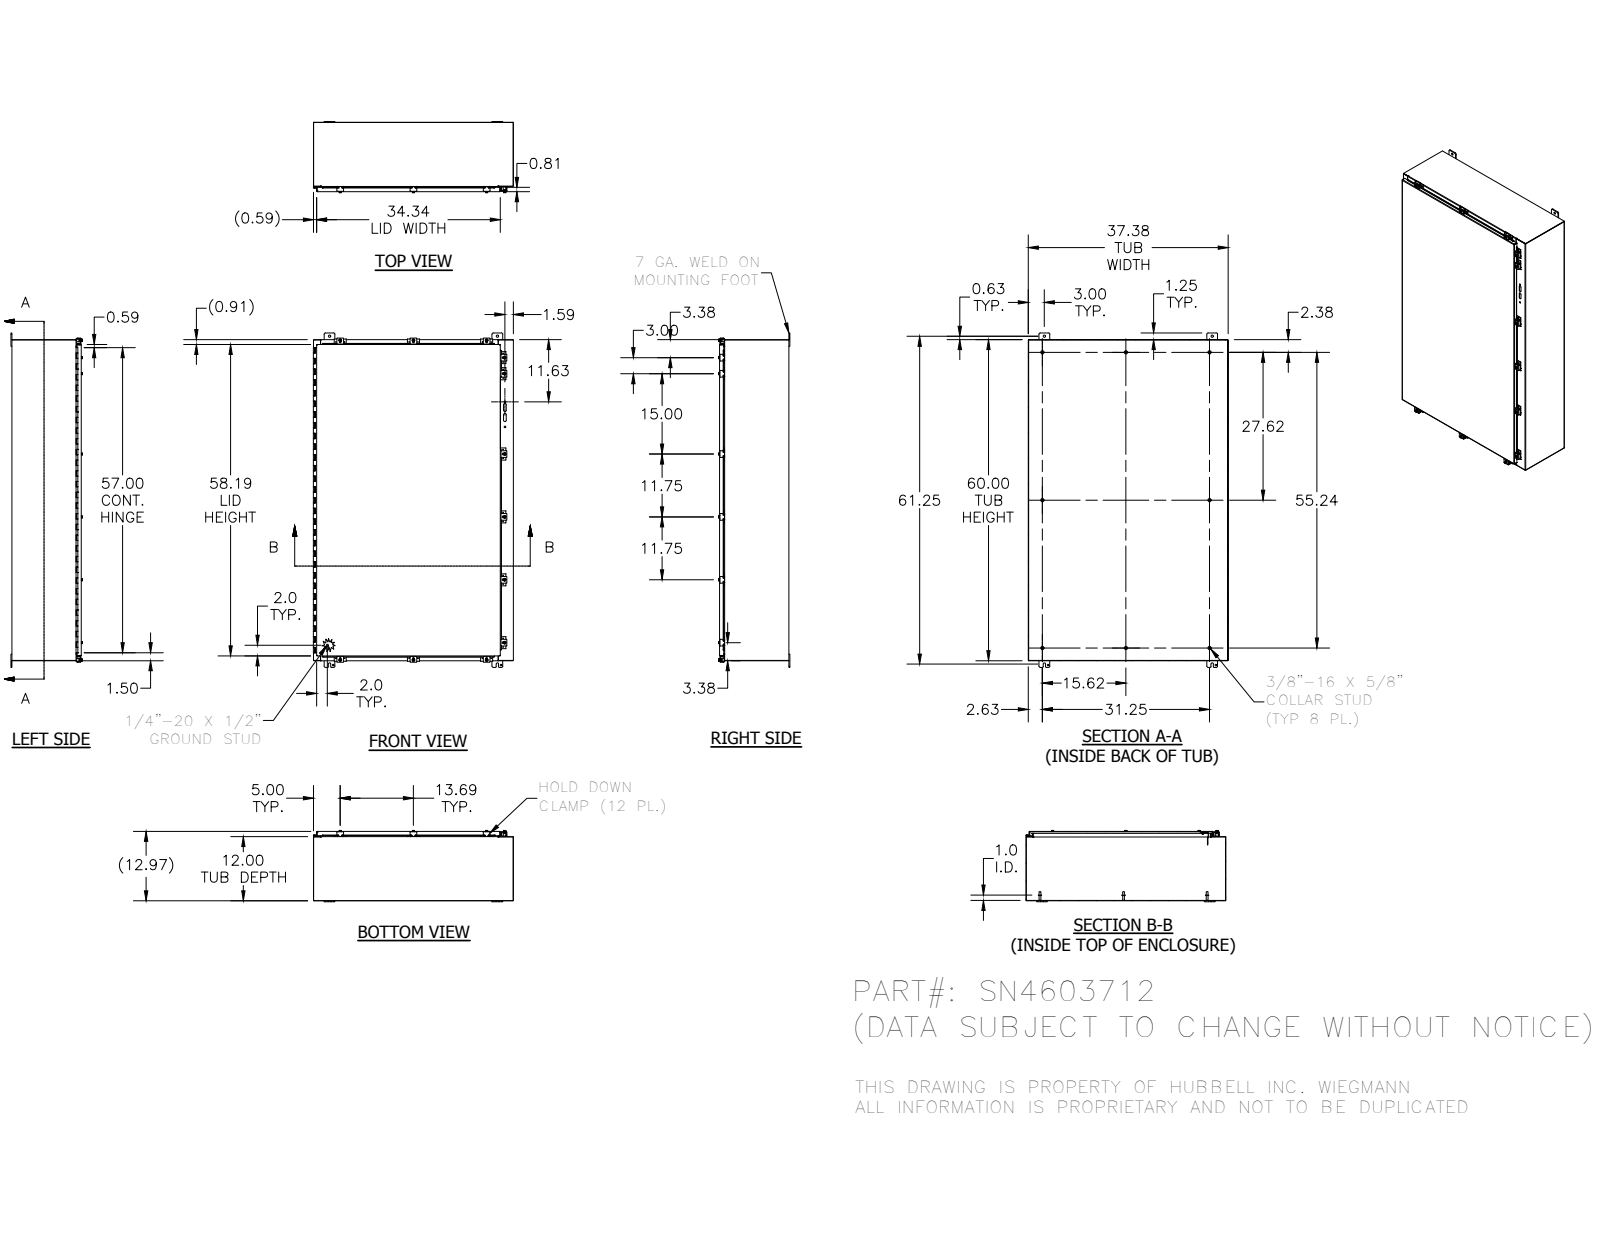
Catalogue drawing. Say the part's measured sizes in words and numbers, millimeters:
The part is named "SN4603712BLR; 3889; 34840; 328116T (+8 more)". Its 3-D file was written by "Autodesk Inventor 2016 (AUTOMOTIVE_DESIGN)". It is 85 solids with 2571 faces: 1391 planar, 842 cylindrical and 338 other. Overall it measures 1587.5 by 949.74 by 338.45 millimeters. Its volume is 9 009 000 cubic millimeters and its surface area 9 615 000 square millimeters. Round holes: 24 of diameter 2.79, 14 of diameter 7.14, 12 of diameter 5.36, 12 of diameter 7.62, 4 of diameter 7.95, 4 of diameter 11.13, 2 of diameter 3.96, 1 of diameter 3.17. Round bosses or shafts: 16 of diameter 6.35, 12 of diameter 13.21, 12 of diameter 12.7, 12 of diameter 8.89, 9 of diameter 8.38, 8 of diameter 15.88, 2 of diameter 4.83, 1 of diameter 8.56. Partial cylindrical surfaces (rounded edges, fillets, slot ends): 139 of radius 0.76, 41 of radius 6.35, 36 of radius 3.17, 25 of radius 1.59, 24 of radius 3.57, 21 of radius 0.79, 21 of radius 2.67, 18 of radius 2.54. The main face-to-face distances are 1.88, 327.59, 325.71, 329.47, 947.45, 1522.12, 945.57, 949.33, 302.92, 24.67. The hole center spacings are 1509.26, 22.26, 347.66, 368.39, 1540.52, 1544.15, 1553.41, 327.14.
